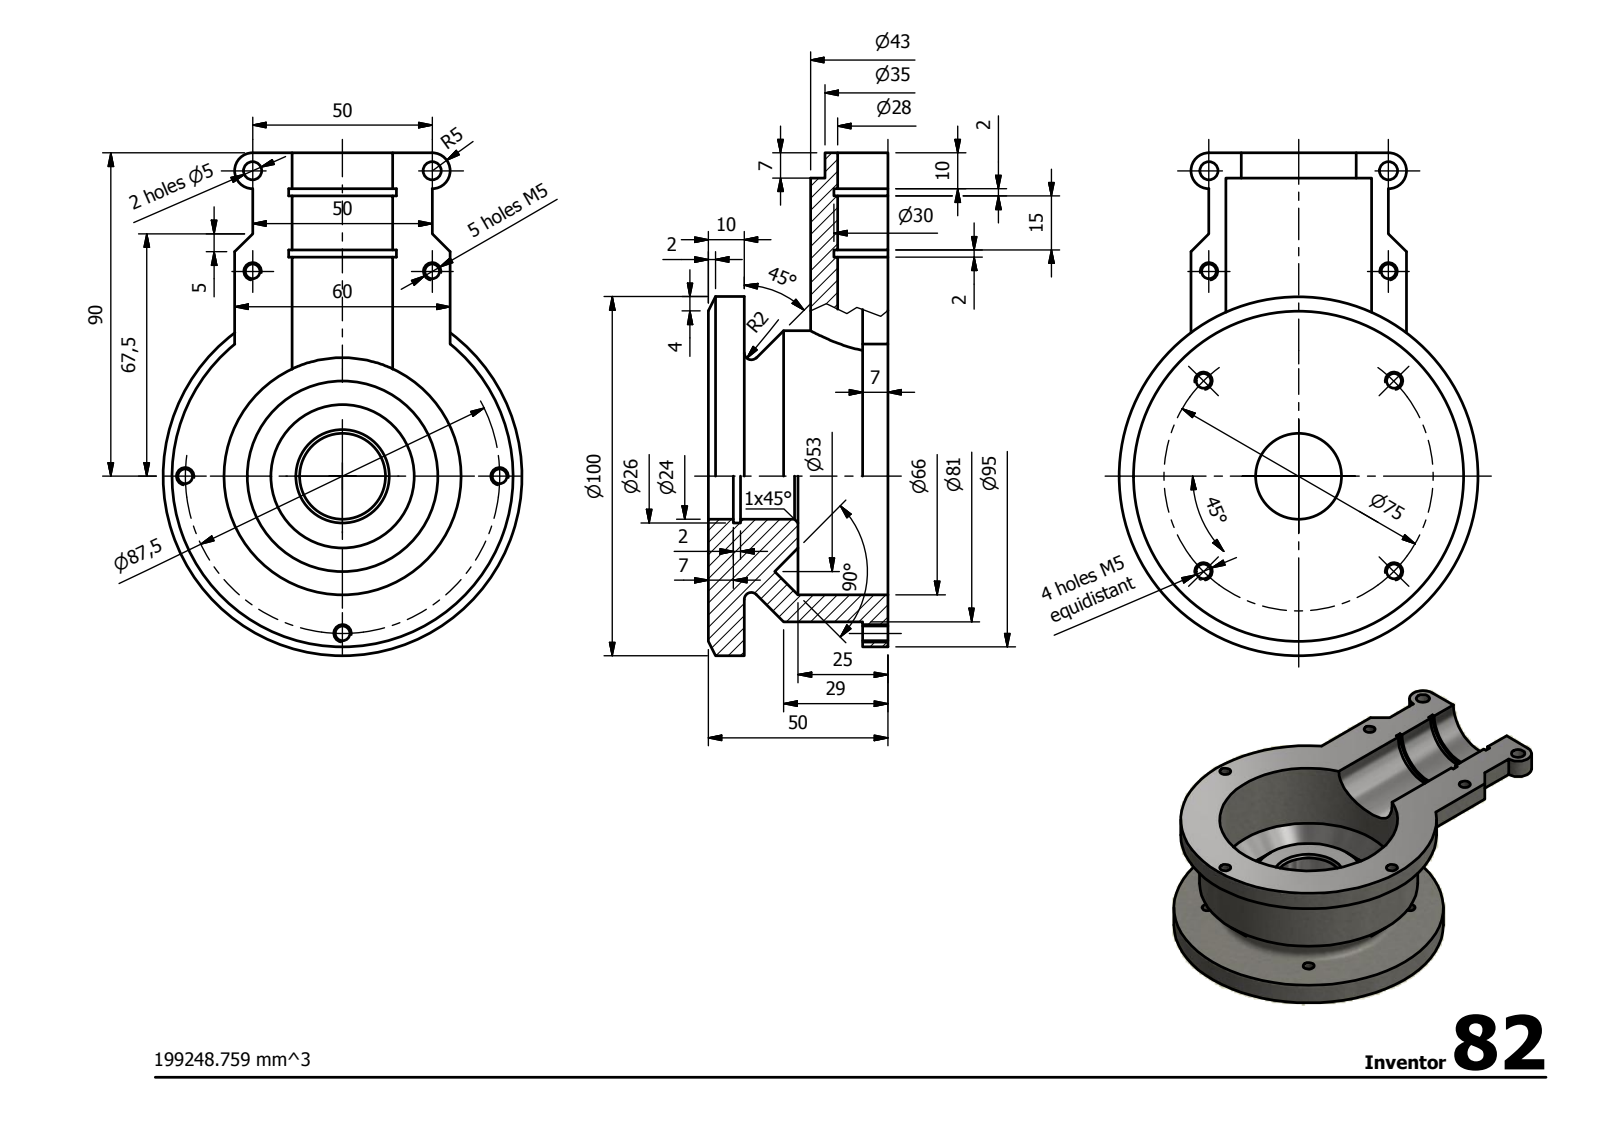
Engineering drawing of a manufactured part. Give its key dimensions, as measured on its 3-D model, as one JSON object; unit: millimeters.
{"step_written_by": "Autodesk Inventor 2014 (AUTOMOTIVE_DESIGN)", "units": "millimeters", "bodies": {"solids": 1, "faces": 52, "planar": 19, "cylindrical": 27, "other": 6}, "overall_size": [140, 100, 50], "volume_mm3": 199222, "surface_area_mm2": 49937, "round_holes": [[4.13, 9], [5, 2], [24, 1], [26, 1], [66, 1]], "round_bosses_or_shafts": [[100, 1], [81, 1]], "partial_cylinders_radius": [[5, 2], [14, 1], [15, 1], [17.5, 1], [21.5, 1], [47.5, 1]], "face_to_face_distances": [50, 10, 40, 7, 43, 33, 25, 18, 15, 5], "hole_center_spacings": [31.63, 75.11, 37.5, 53.04, 43.75, 28, 30.52, 50]}
